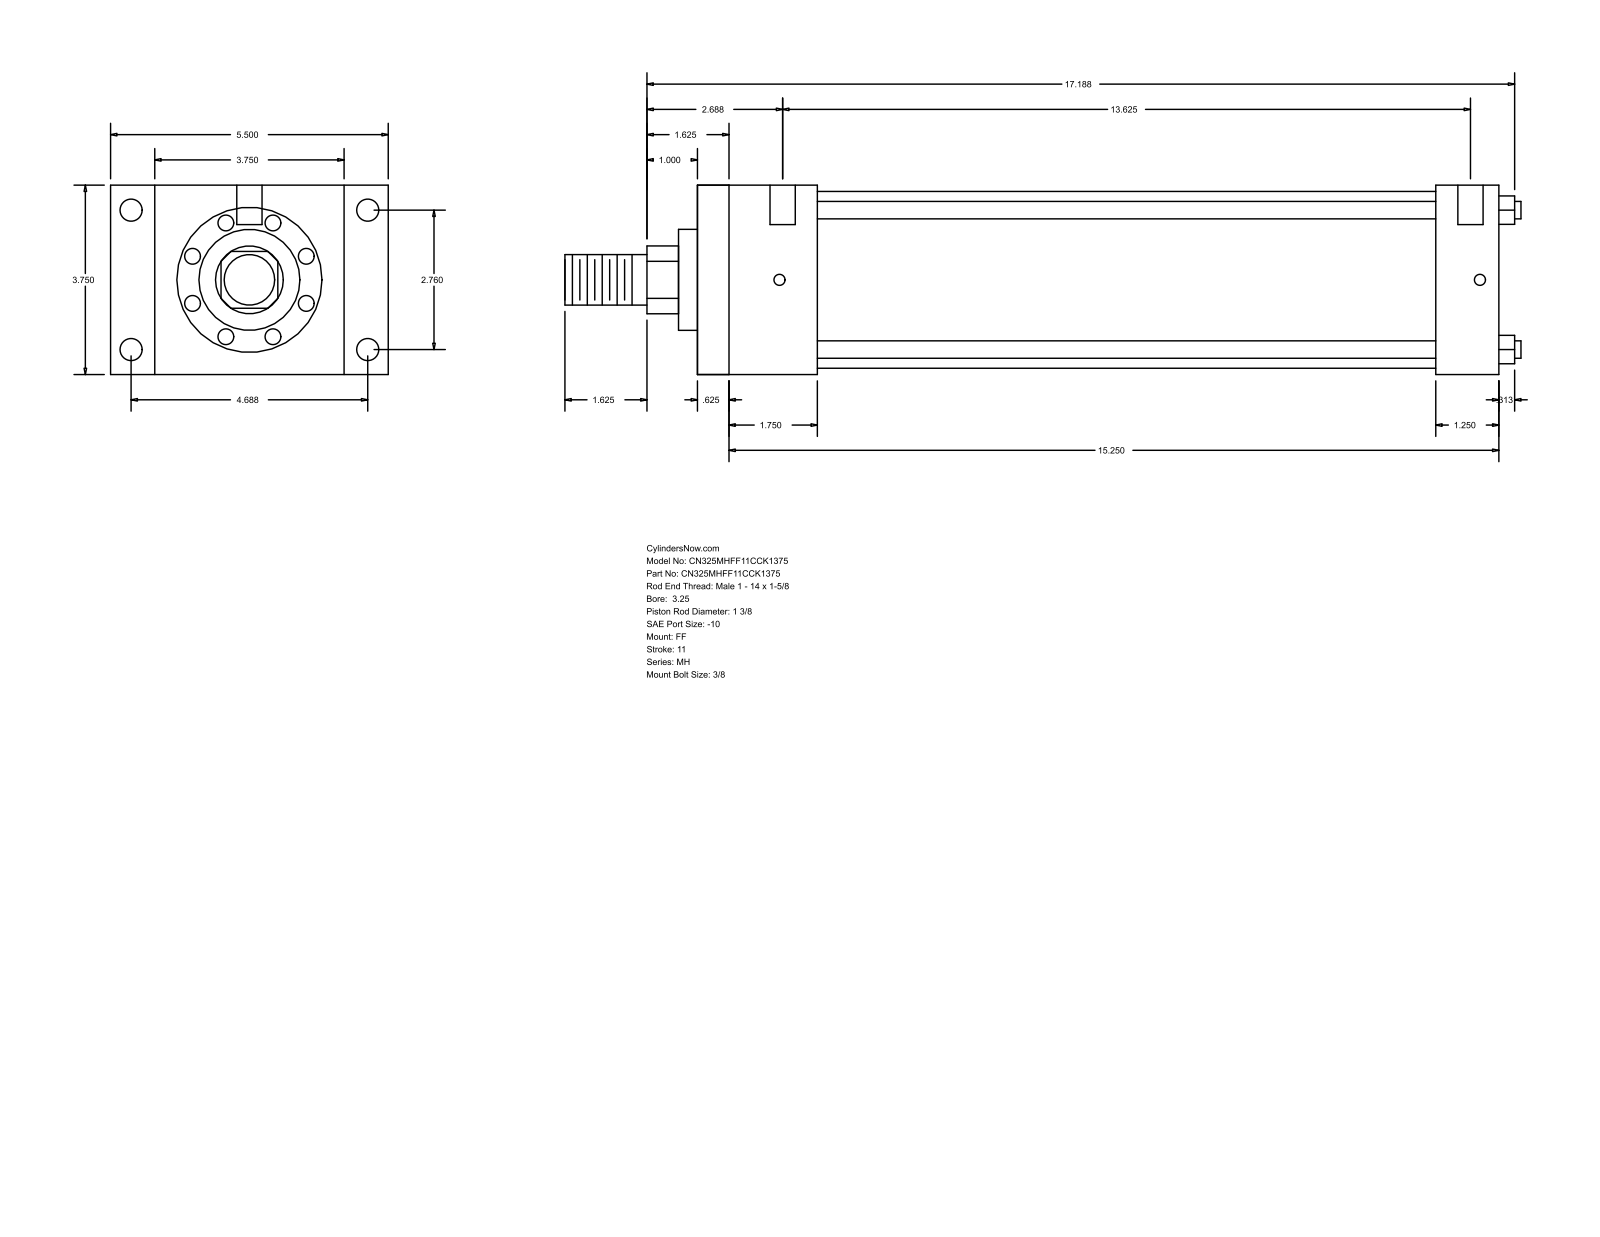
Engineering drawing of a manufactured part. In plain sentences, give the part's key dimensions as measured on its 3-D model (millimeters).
The part is named "MH_FF__0325_1.375". Its 3-D file was written by "GSSL Pune (CONFIG_CONTROL_DESIGN)". It is 0 solids with 92 faces: 64 planar, 28 cylindrical and 0 other. Overall it measures 481.01 by 139.7 by 95.25 millimeters. Round holes: 4 of diameter 5.56, 4 of diameter 11.13, 2 of diameter 12.7. Round bosses or shafts: 4 of diameter 8.76, 1 of diameter 88.9, 1 of diameter 50.8, 1 of diameter 34.92, 1 of diameter 25.4. Partial cylindrical surfaces (rounded edges, fillets, slot ends): 1 of radius 17.06. The main face-to-face distances are 95.24, 403.22, 15.87, 387.35, 22.23, 117.47, 371.48, 355.61, 31.74, 60.32. The hole center spacings are 70.1, 119.06, 138.16, 352.43, 1.59, 4.76, 346.08, 347.67.
